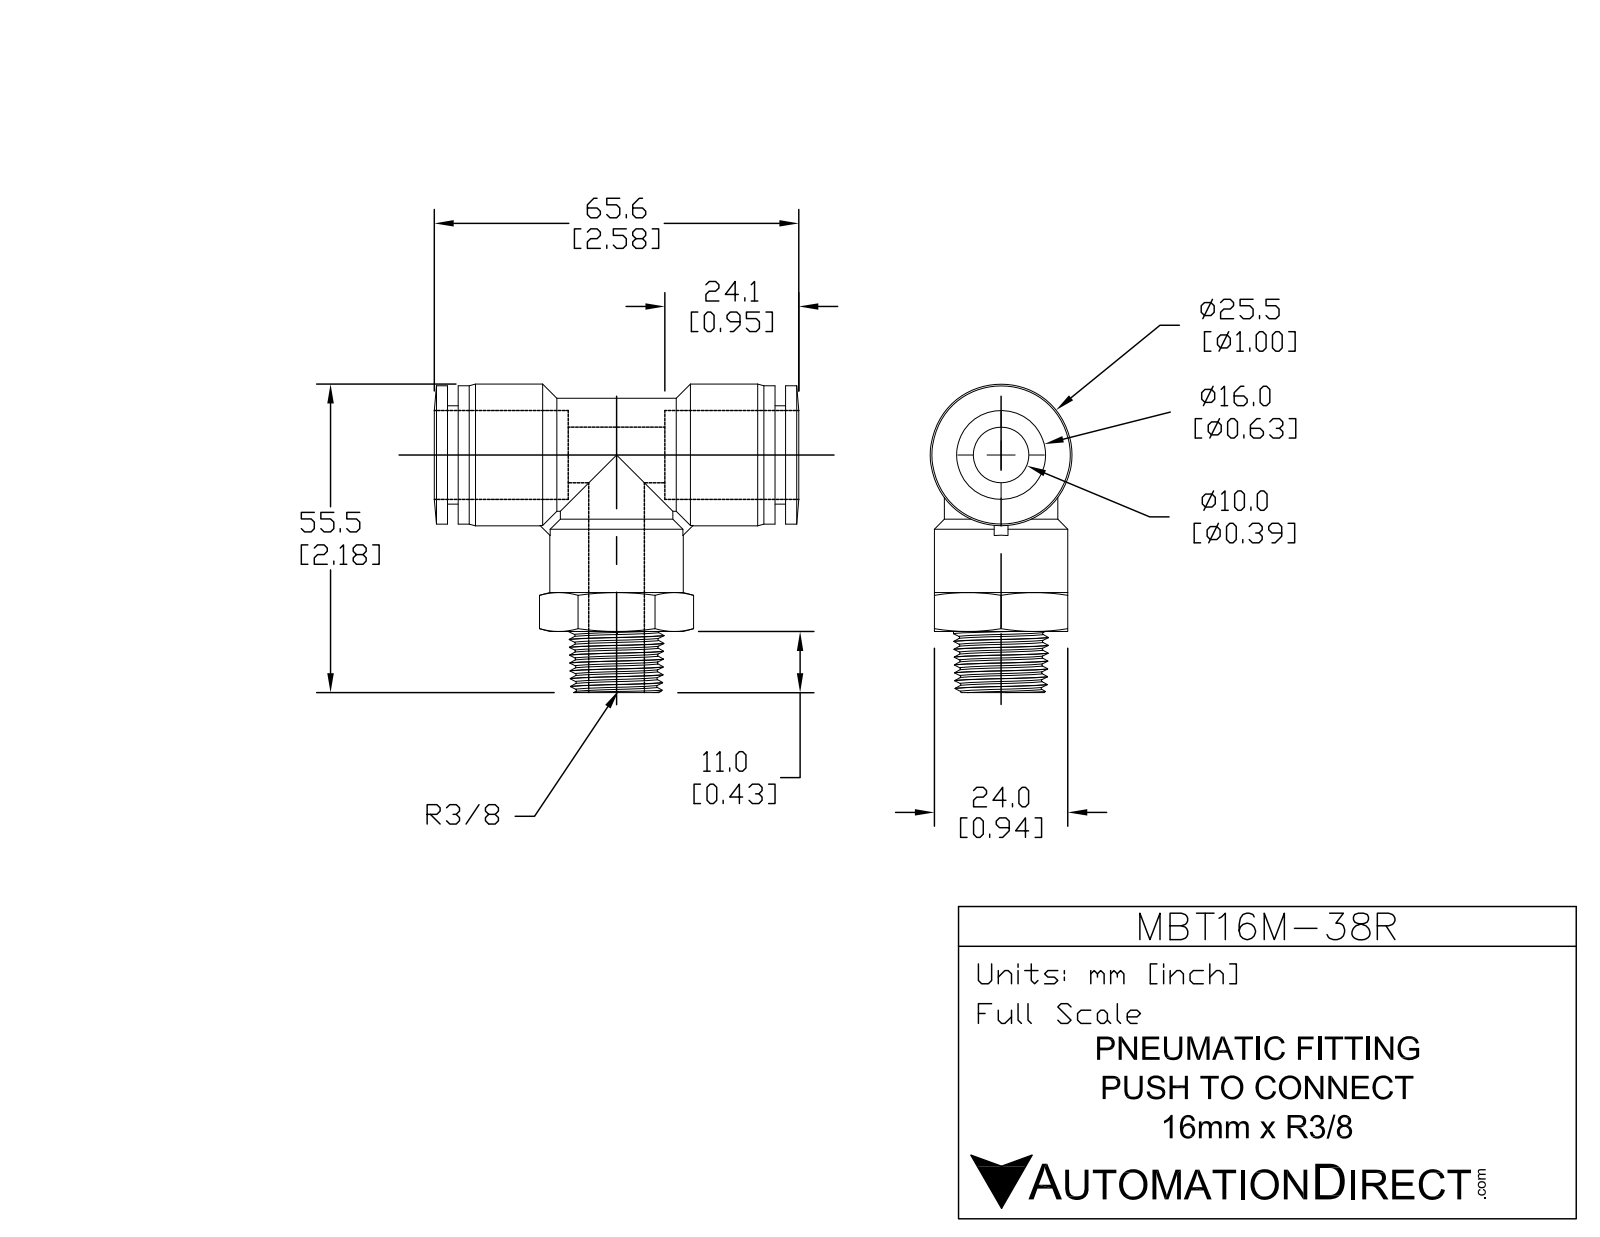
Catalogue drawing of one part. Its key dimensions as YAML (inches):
part_name: "MBT16M-38R"
step_written_by: "SolidWorks 2015 (AUTOMOTIVE_DESIGN)"
units: inches
bodies: {solids: 1, faces: 100, planar: 20, cylindrical: 35, other: 45}
overall_size: [2.583, 2.187, 1.004]
volume: 1.588
surface_area: 20.42
round_holes:
  - {diameter: 0.394, count: 2}
  - {diameter: 0.642, count: 1}
round_bosses_or_shafts:
  - {diameter: 0.803, count: 2}
  - {diameter: 1.004, count: 1}
  - {diameter: 0.992, count: 1}
  - {diameter: 0.984, count: 1}
  - {diameter: 0.945, count: 1}
  - {diameter: 0.709, count: 1}
face_to_face_distances: [0.945, 0.839, 1.524, 0.063, 2.299, 0.776, 1.461, 2.362, 0.685, 2.236]
